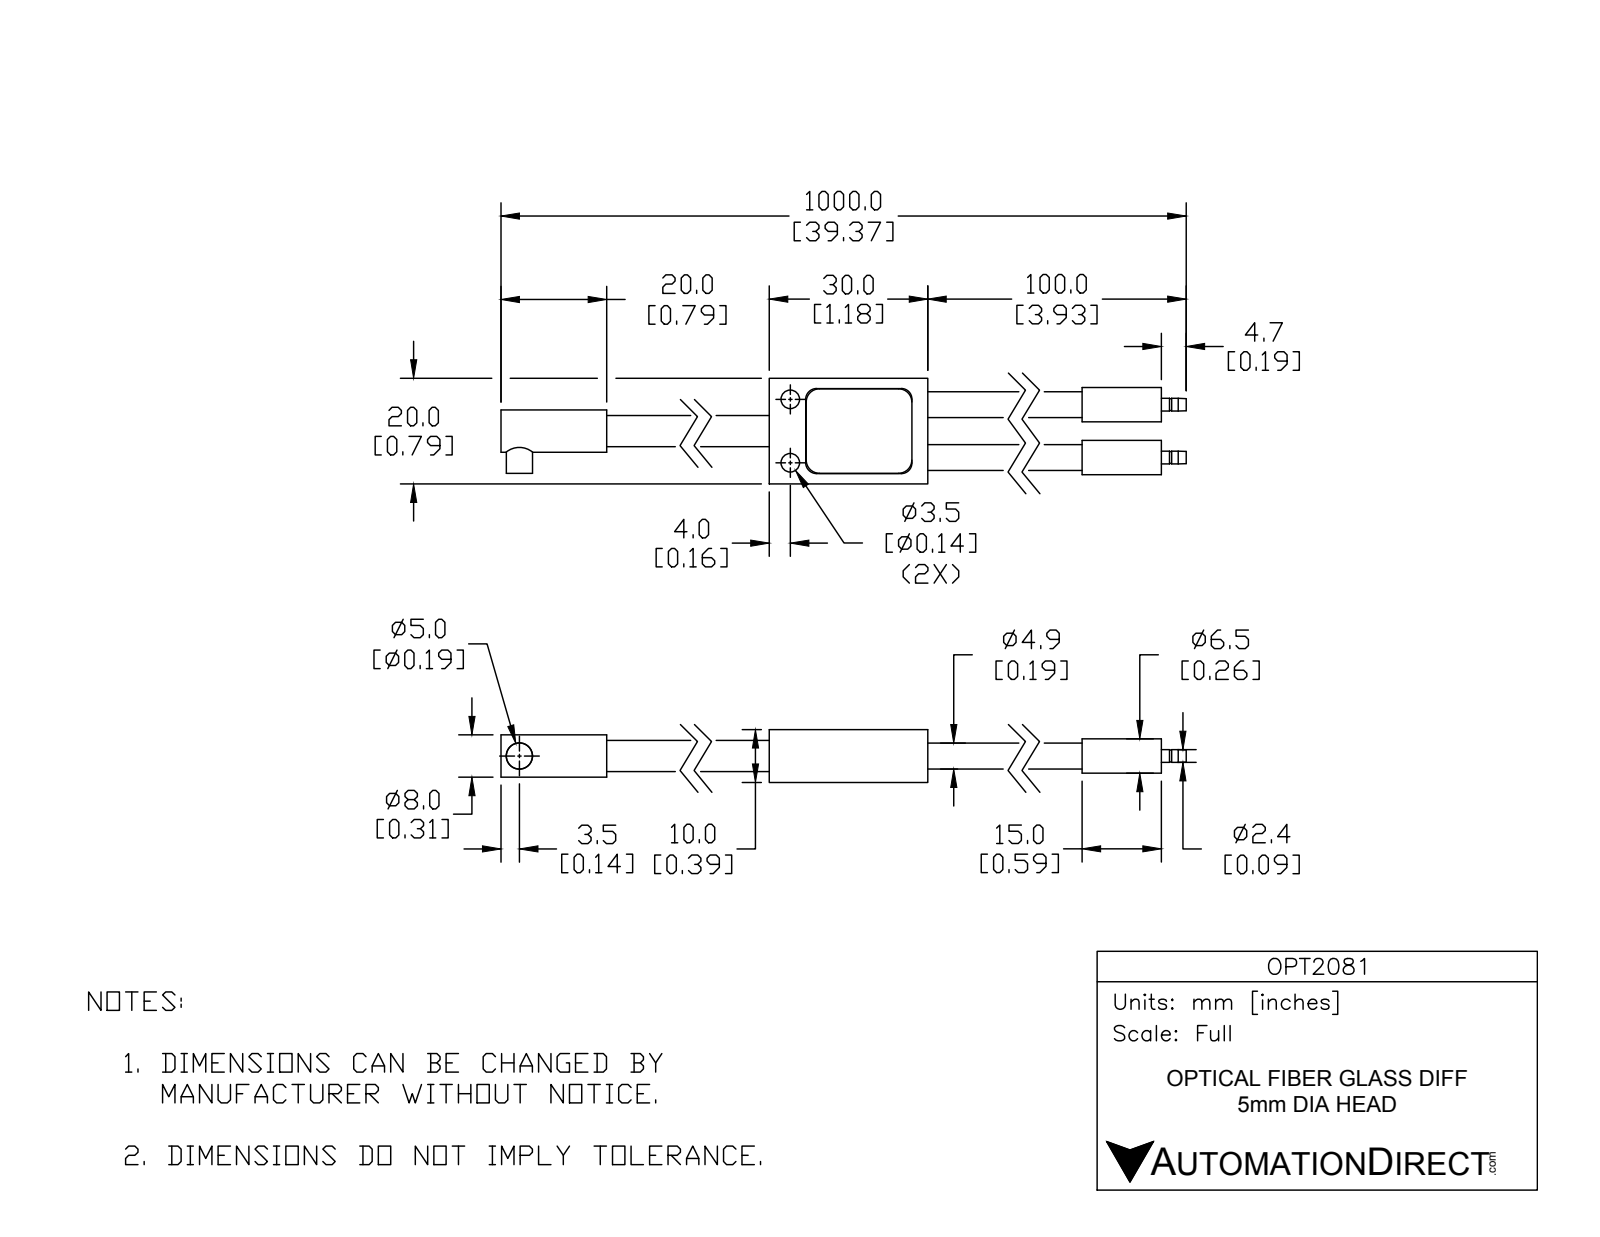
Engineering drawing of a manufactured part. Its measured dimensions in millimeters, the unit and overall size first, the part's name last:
Units: millimetres
Overall size (bounding box): 1000 × 20 × 10
Round holes (diameter × count): ⌀3.5 ×2, ⌀5 ×1
Round bosses / shafts (diameter × count): ⌀6.5 ×2, ⌀4.9 ×2, ⌀2.4 ×2, ⌀8 ×1, ⌀5.9 ×1, ⌀5 ×1
Partial cylindrical surfaces — rounded edges, fillets, slot ends (radius × count): R2.5 ×4, R2 ×2, R2.1 ×2, R3.5 ×1
Main face-to-face distances: 20, 9.9, 10, 30, 125.3, 95.3, 870, 900, 995.3, 980.3
Hole centre spacings: 12
Volume: 34 170 mm³ · Surface area: 22 010 mm²
Bodies: 1 solid, 85 faces (28 planar, 45 cylindrical, 12 other)
Part name (STEP PRODUCT): OPT2081
STEP written by: SolidWorks 2014 (AUTOMOTIVE_DESIGN)
